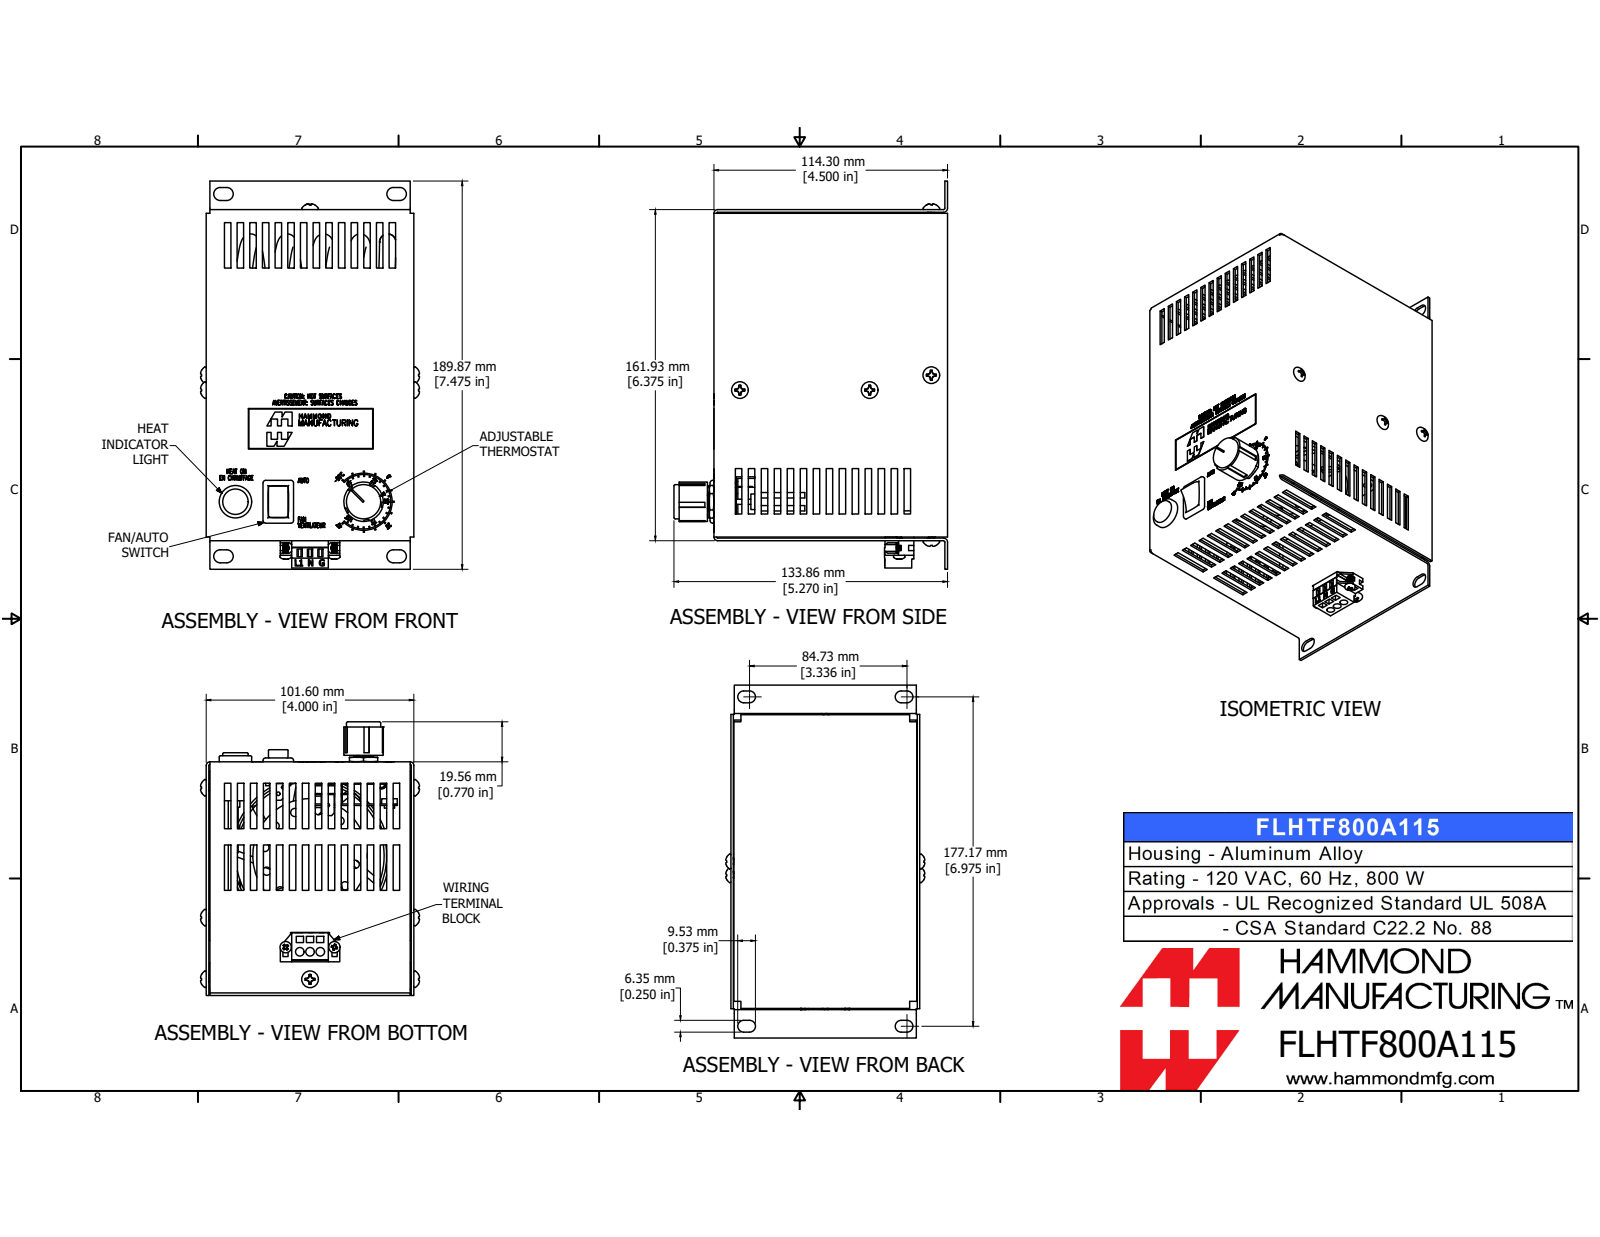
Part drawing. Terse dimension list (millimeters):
name: FLHTF800A115
written by: SolidWorks 2019 (AUTOMOTIVE_DESIGN)
unit: mm
bodies: 17 solids, 4227 faces (3719 planar, 274 cylindrical, 234 other)
size: 189.9 × 133.9 × 107.1
volume: 180 700 mm³; area: 222 600 mm²
holes: 4× ⌀3.5, 4× ⌀4.6, 4× ⌀5.2, 3× ⌀4.2, 2× ⌀2.2, 2× ⌀3, 2× ⌀3.3, 2× ⌀4.8, 1× ⌀1.7, 1× ⌀1.8, 1× ⌀6.4, 1× ⌀9.7
bosses: 4× ⌀4.2, 4× ⌀2.6, 2× ⌀4.3, 2× ⌀2.7, 1× ⌀19.3, 1× ⌀16.8, 1× ⌀16.5, 1× ⌀15.9
rounds: 38× R3.2, 17× R1.3, 12× R16, 9× R3.8, 8× R0.6, 4× R0.5, 4× R1.8, 2× R0.4
face distances: 1.3, 100.3, 2.5, 1.3, 160.6, 101.6, 99, 112.8, 114.1, 110.3
hole spacings: 70, 5, 7.3, 12.1, 14.3, 14.4, 17.1, 19.7
